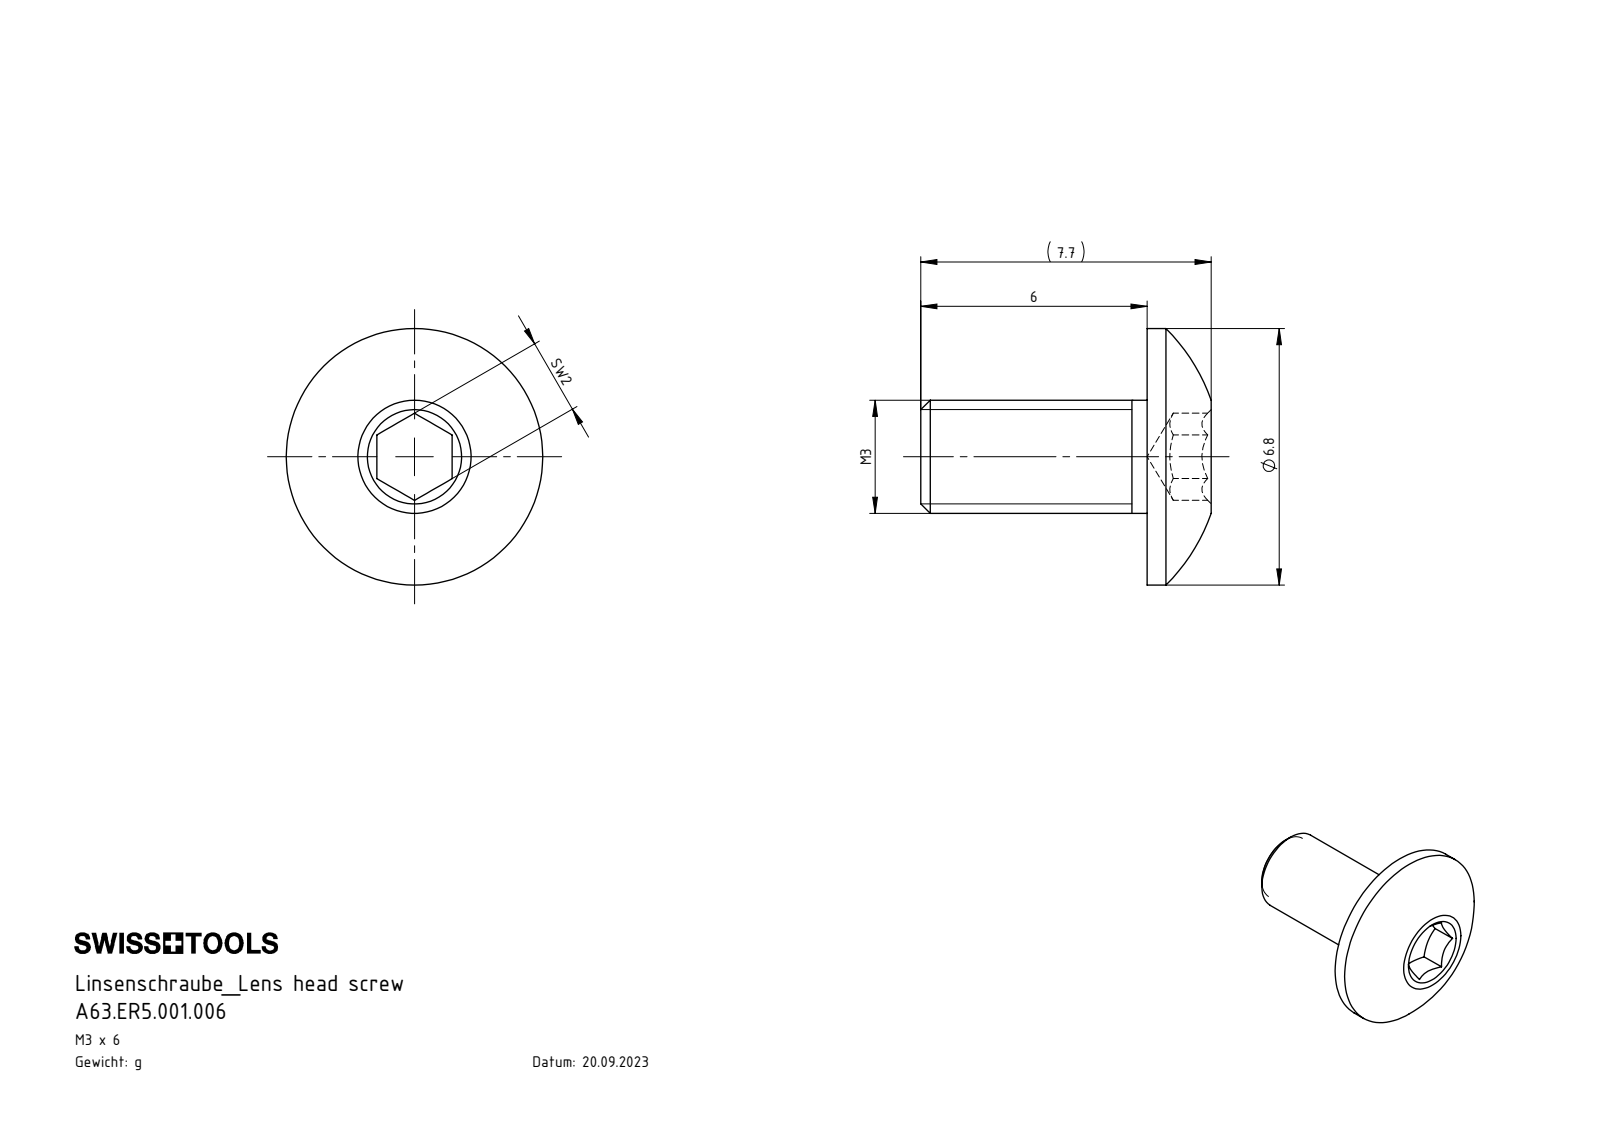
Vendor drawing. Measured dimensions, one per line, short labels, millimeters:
name: A63.ER5.001.006
written by: SolidWorks 2017 (AUTOMOTIVE_DESIGN)
unit: mm
bodies: 1 solid, 21 faces (9 planar, 4 cylindrical, 8 other)
size: 7.7 × 6.8 × 6.8
volume: 82 mm³; area: 152 mm²
bosses: 1× ⌀6.8, 1× ⌀3
face distances: 6, 2, 1.7, 7.7
